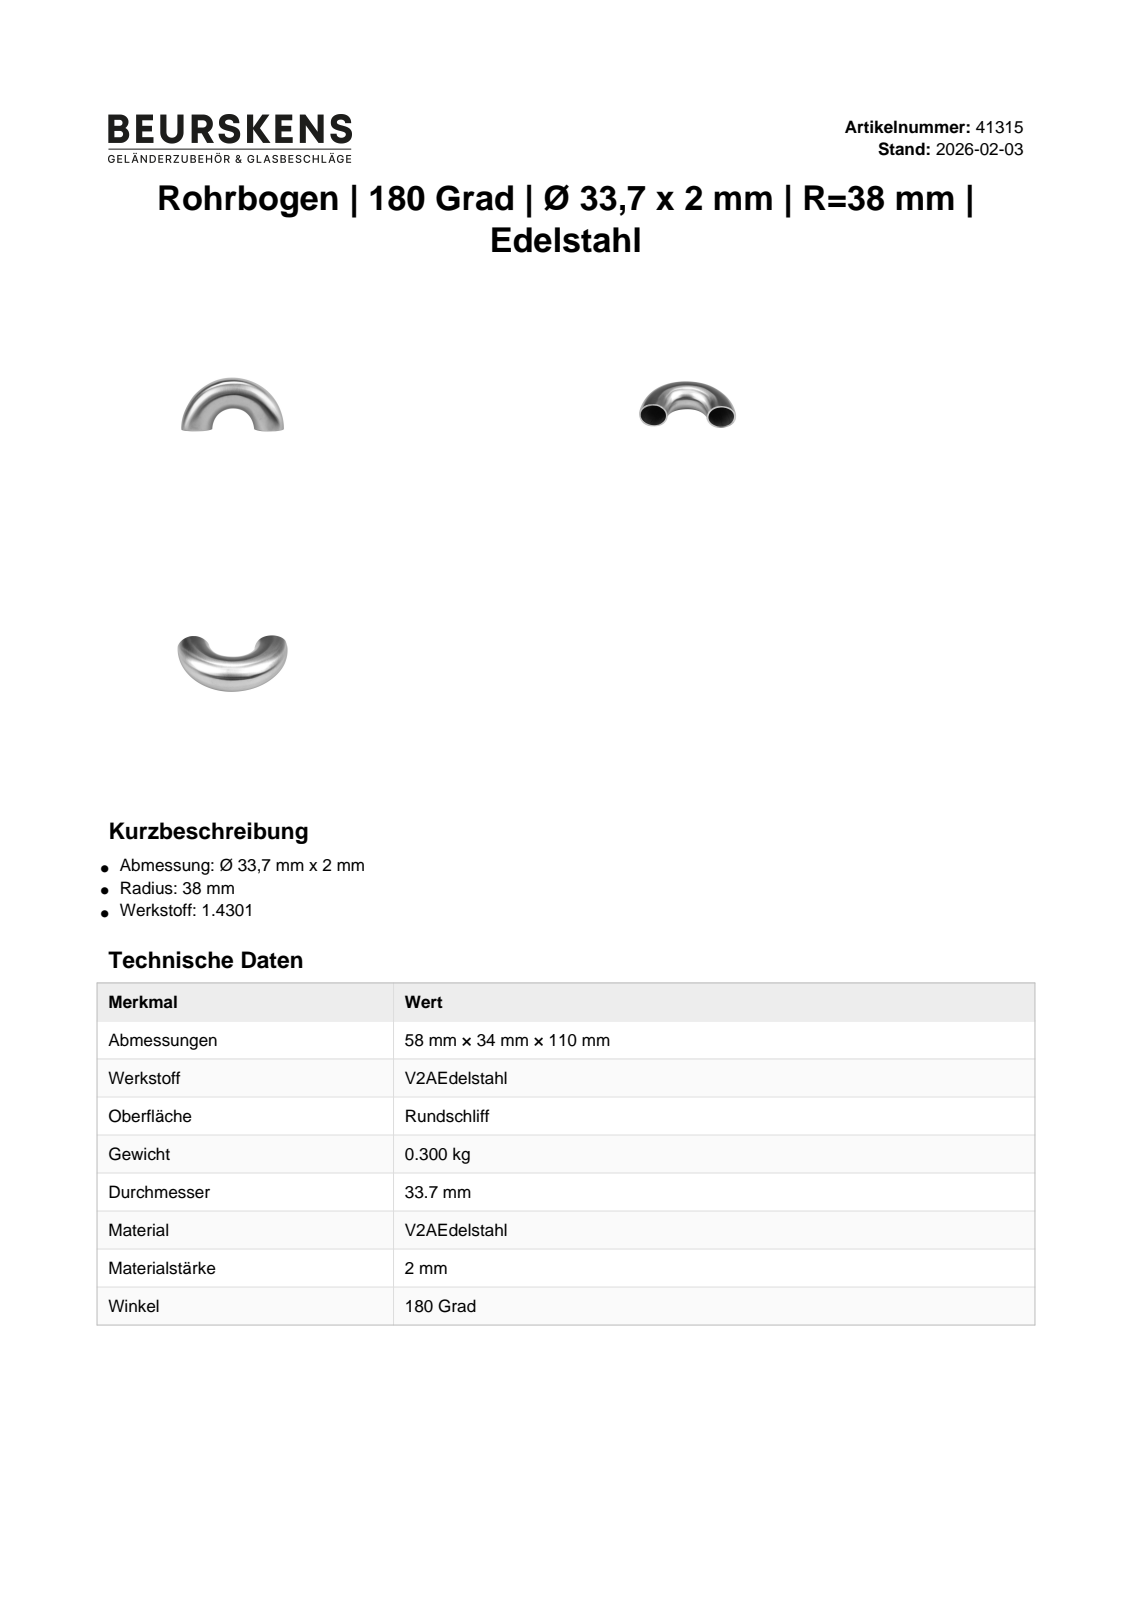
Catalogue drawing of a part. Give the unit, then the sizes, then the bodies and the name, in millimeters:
Units: millimetres
Overall size (bounding box): 109.7 × 54.85 × 33.7
Volume: 23 778 mm³ · Surface area: 24 176 mm²
Bodies: 1 solid, 4 faces (2 planar, 0 cylindrical, 2 other)
Part name (STEP PRODUCT): 41315
STEP written by: Autodesk Inventor 2022 (AUTOMOTIVE_DESIGN)
